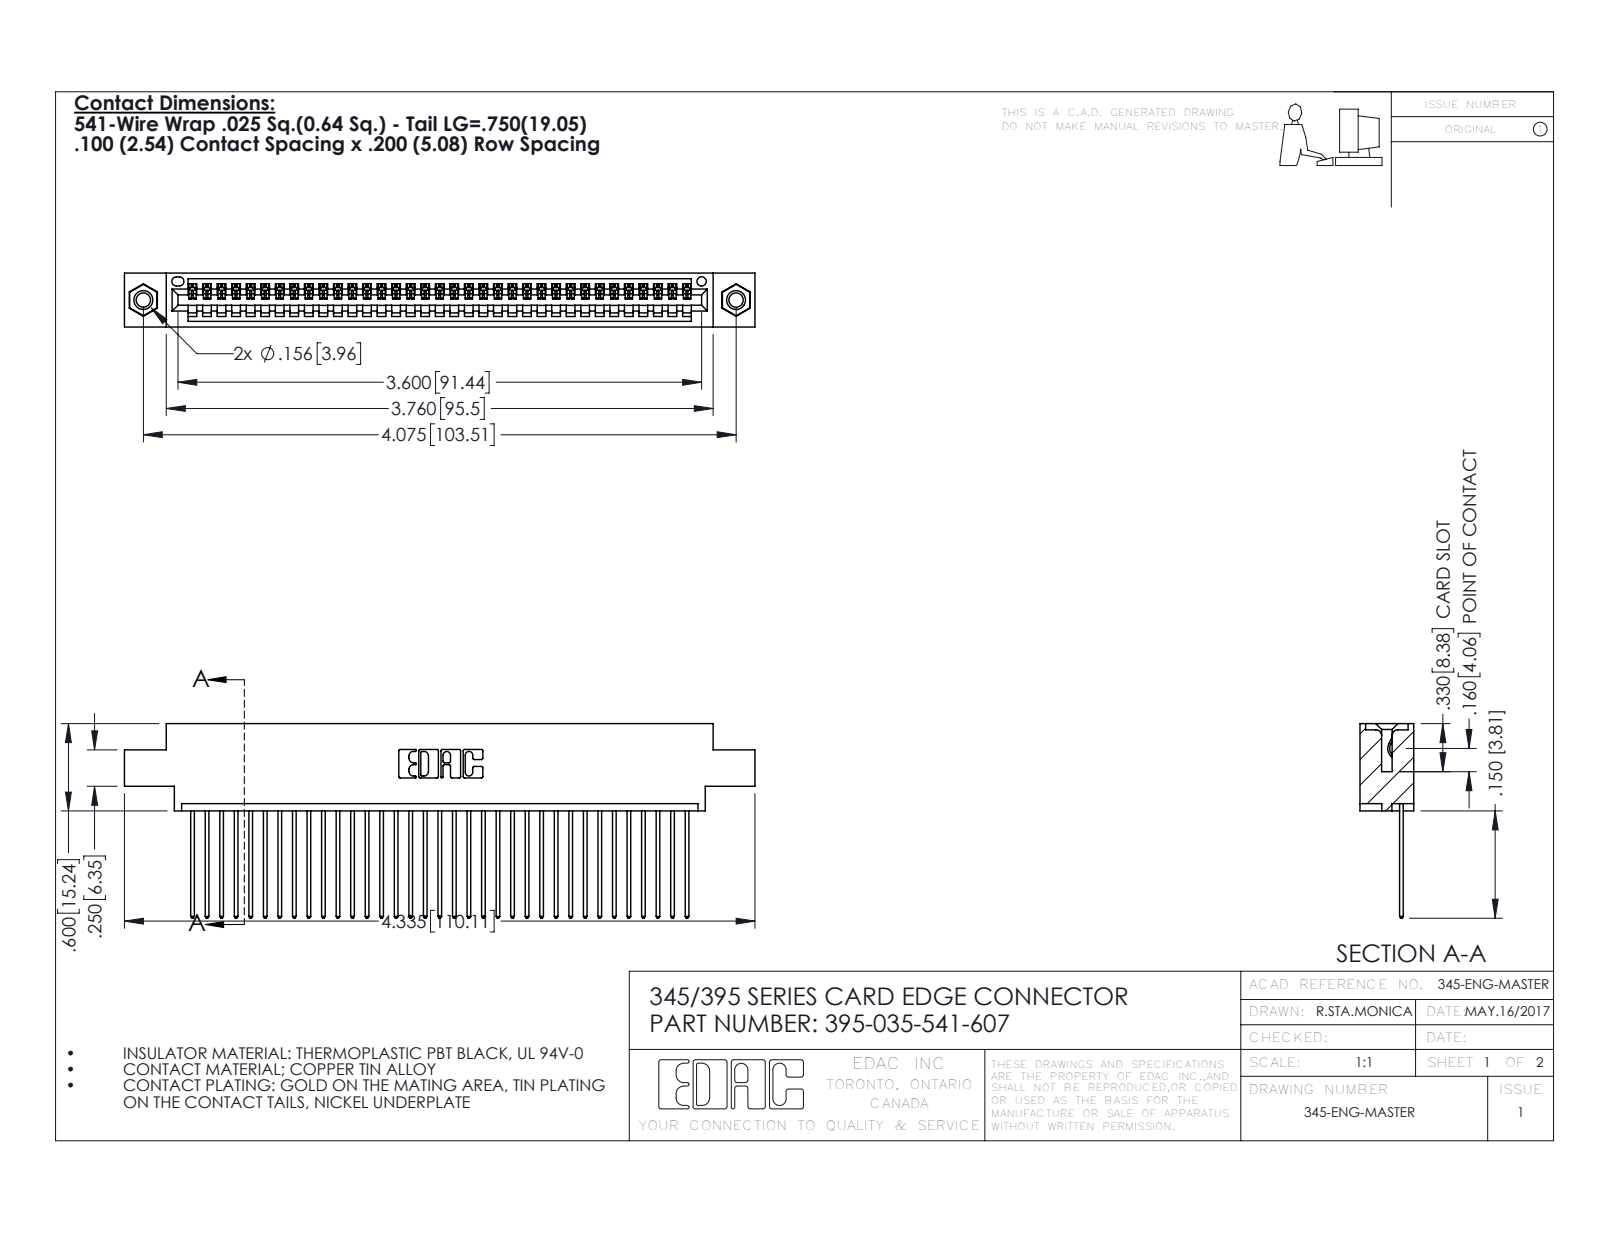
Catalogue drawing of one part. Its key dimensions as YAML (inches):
part_name: "345 Part_0.170 Offset - 0.156 Dia-TI; 345-250-001_345-250-005-103; 345-292-001_345-293-141; 395-035-541-607"
step_written_by: "SolidWorks 2016 (CONFIG_CONTROL_DESIGN)"
units: inches
bodies: {solids: 38, faces: 2220, planar: 1516, cylindrical: 688, other: 16}
overall_size: [4.335, 1.337, 0.37]
volume: 0.634
surface_area: 22.55
round_holes:
  - {diameter: 0.098, count: 2}
  - {diameter: 0.125, count: 2}
  - {diameter: 0.156, count: 2}
  - {diameter: 0.064, count: 1}
round_bosses_or_shafts:
  - {diameter: 0.155, count: 2}
partial_cylinders:
  - {radius: 0.006, count: 70}
  - {radius: 0.01, count: 70}
  - {radius: 0.01, count: 22}
  - {radius: 0.007, count: 6}
  - {radius: 0.031, count: 6}
  - {radius: 0.026, count: 3}
  - {radius: 0.031, count: 2}
  - {radius: 0.04, count: 2}
face_to_face_distances: [0.072, 0.298, 0.37, 0.098, 0.272, 0.025, 0.2, 0.225, 0.175, 0.149]
hole_center_spacings: [0.27, 3.839, 4.075]
